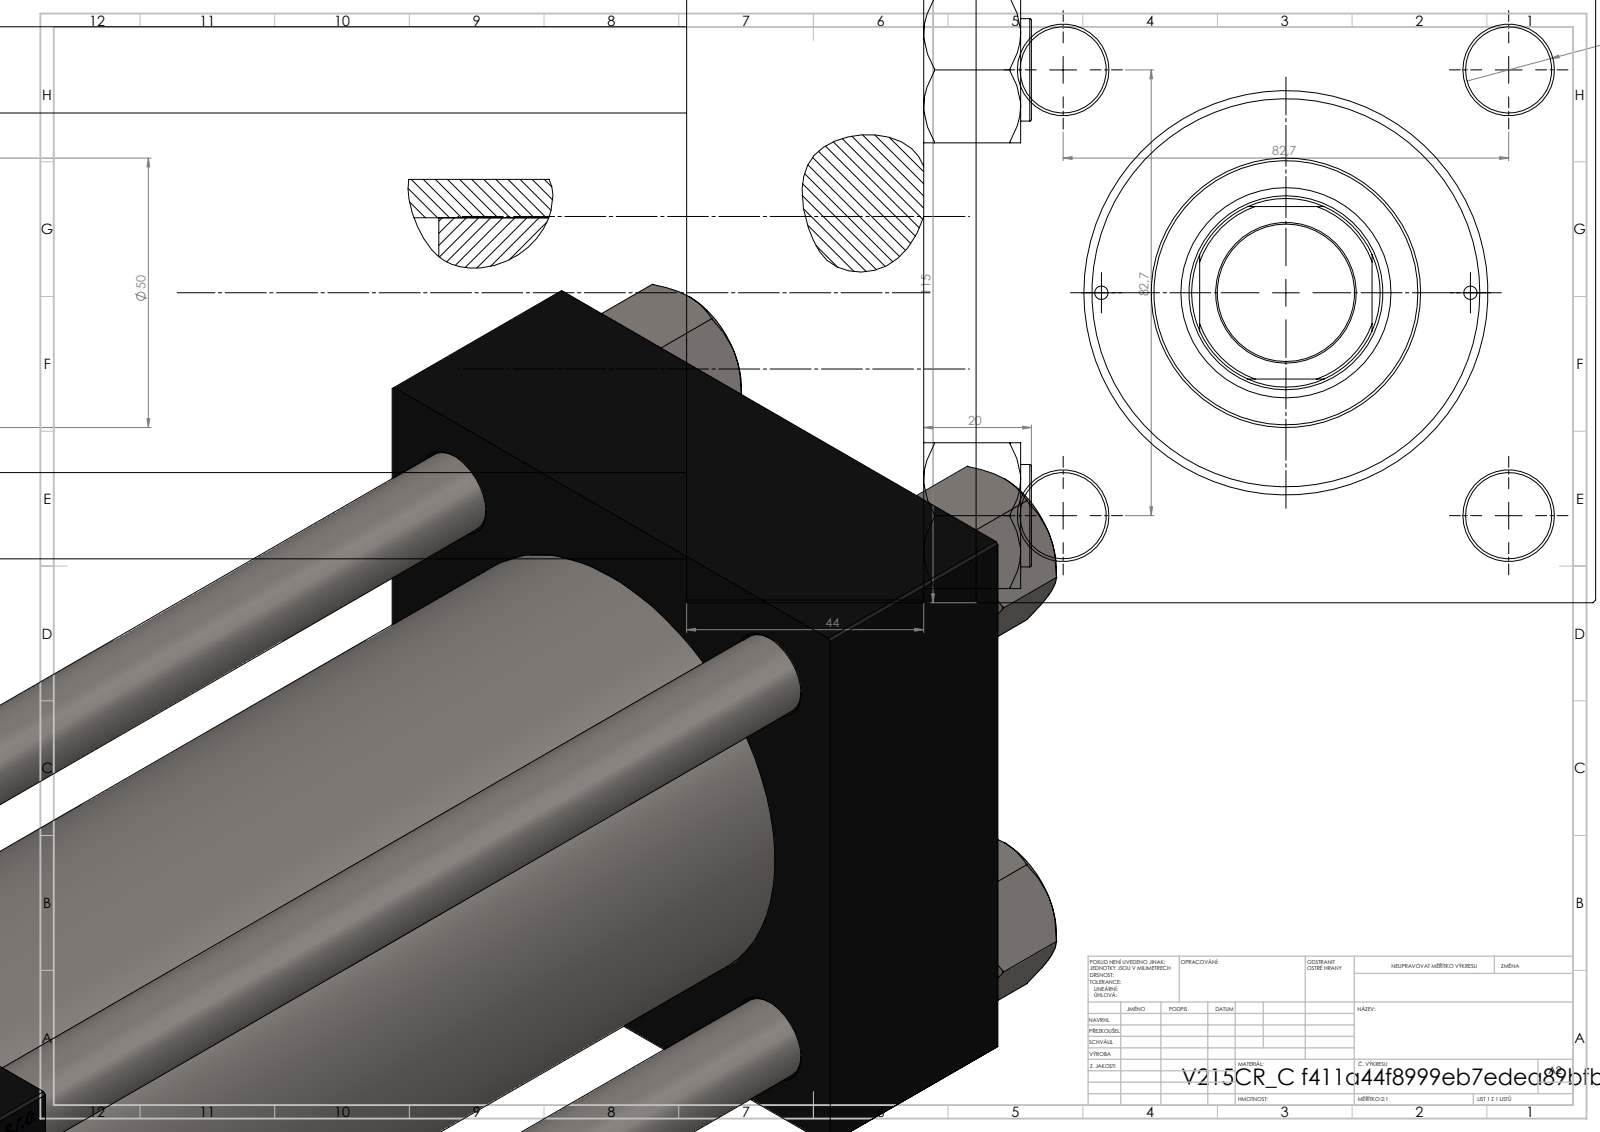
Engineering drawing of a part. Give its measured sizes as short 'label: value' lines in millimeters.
name: NUT_M5_C; V215_VC_A; V215CR_C_Body; V215CR_C_TYCINKA (+1 more)
written by: SolidWorks 2019 (CONFIG_CONTROL_DESIGN)
unit: mm
bodies: 11 solids, 1202 faces (576 planar, 90 cylindrical, 536 other)
size: 370 × 115 × 115
volume: 2 151 000 mm³; area: 385 504 mm²
holes: 4× ⌀16, 2× ⌀2.5, 2× ⌀7, 2× ⌀26.44, 2× ⌀35, 1× ⌀25.5, 1× ⌀36, 1× ⌀39, 1× ⌀61, 1× ⌀72, 1× ⌀80
bosses: 4× ⌀19, 1× ⌀86, 1× ⌀50
rounds: 1× R17.5
face distances: 115, 44, 319, 275, 250, 206, 69, 290.3, 246.3, 40.3
hole spacings: 41.96, 58.48, 82.7, 86.17, 34.25, 116.96, 68.5, 251
